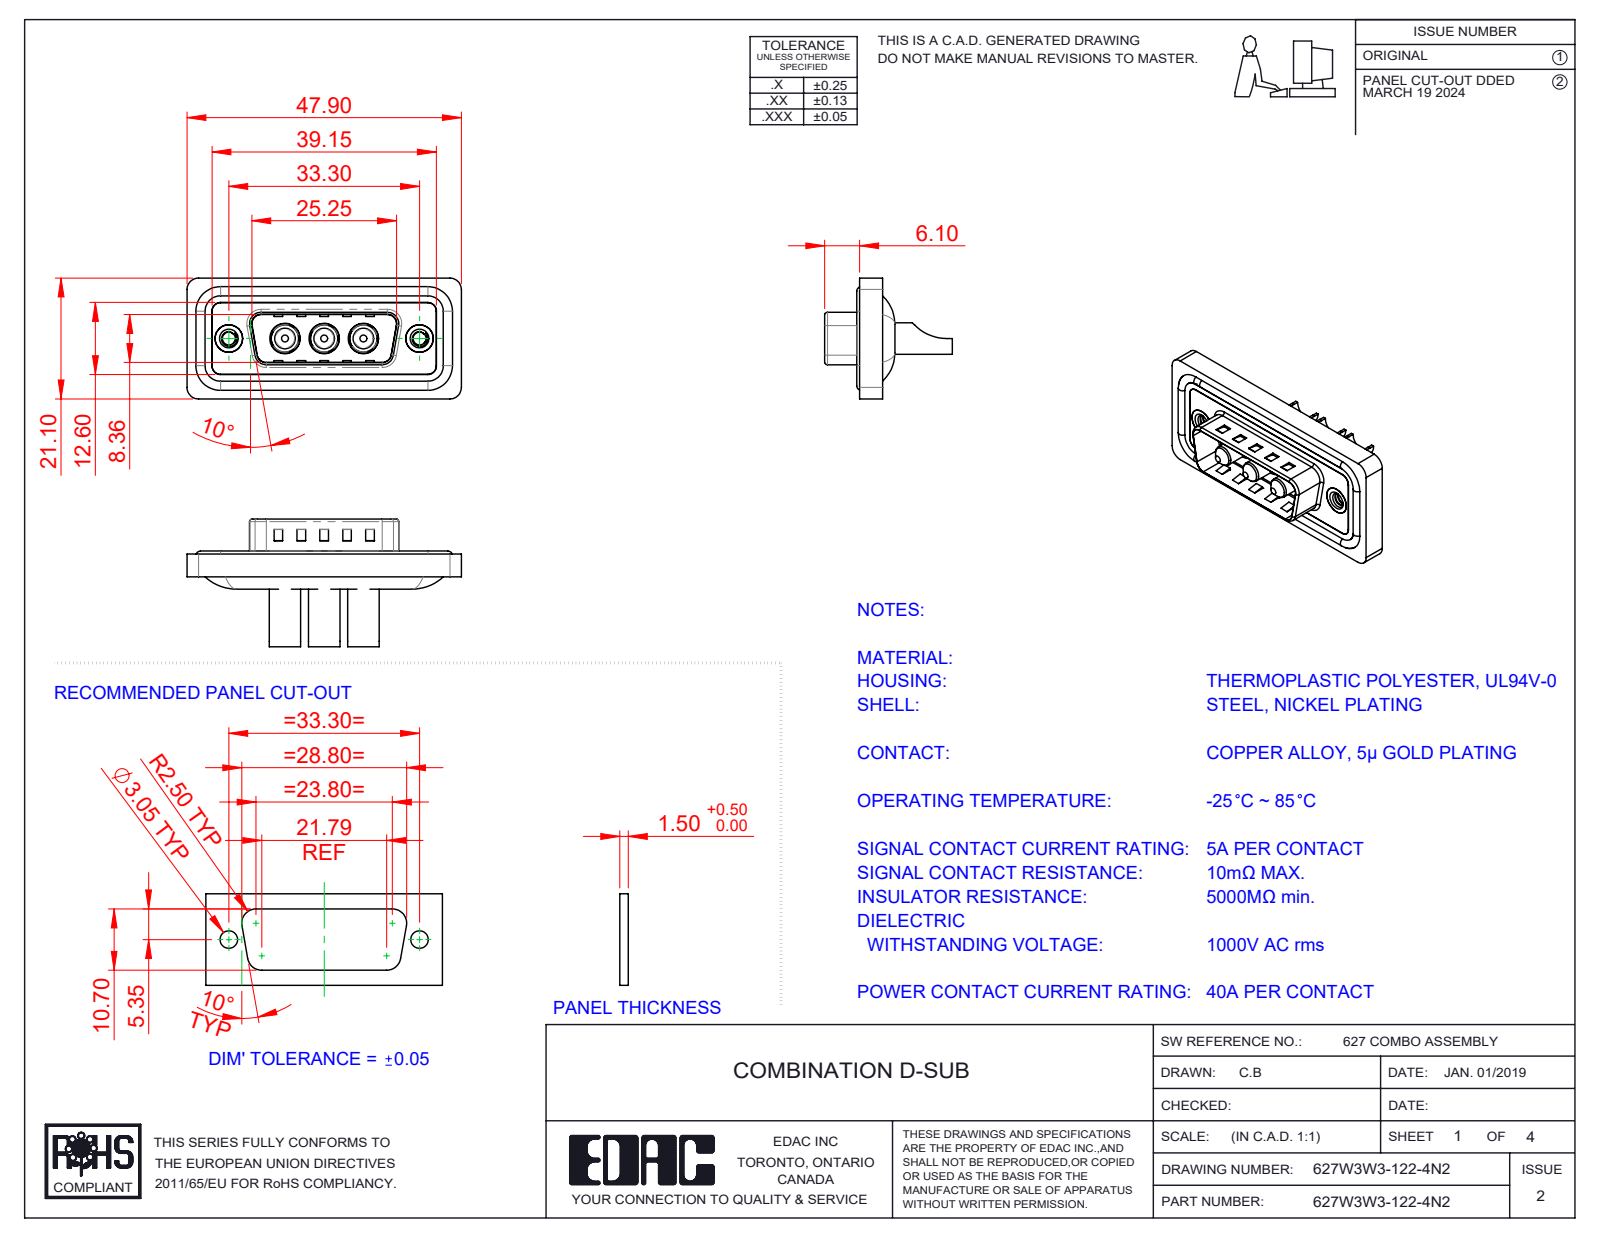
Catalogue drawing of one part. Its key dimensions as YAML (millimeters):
part_name: "Power Pin_40A SC; 627Combo Shell Rear_15 Contacts; 627Combo Threaded Rivet_2; 627Combo Shell Front_15 Contacts (+3 more)"
step_written_by: "SolidWorks 2023 (CONFIG_CONTROL_DESIGN)"
units: millimeters
bodies: {solids: 13, faces: 573, planar: 213, cylindrical: 244, other: 116}
overall_size: [47.9, 22.3, 21.1]
volume: 5705
surface_area: 9173
round_holes:
  - {diameter: 4.6, count: 3}
  - {diameter: 4.85, count: 3}
  - {diameter: 5.3, count: 3}
  - {diameter: 2.26, count: 2}
  - {diameter: 4, count: 2}
  - {diameter: 4.8, count: 2}
  - {diameter: 5, count: 2}
round_bosses_or_shafts:
  - {diameter: 1.6, count: 4}
  - {diameter: 5.5, count: 3}
  - {diameter: 5.2, count: 3}
  - {diameter: 4.75, count: 3}
  - {diameter: 3.75, count: 3}
  - {diameter: 3.6, count: 3}
  - {diameter: 4.9, count: 2}
partial_cylinders:
  - {radius: 1.5, count: 26}
  - {radius: 2, count: 20}
  - {radius: 0.5, count: 8}
  - {radius: 1.6, count: 8}
  - {radius: 0.25, count: 4}
  - {radius: 0.6, count: 4}
  - {radius: 0.65, count: 4}
  - {radius: 0.9, count: 4}
face_to_face_distances: [0.4, 1.1, 0.5, 1.6, 3.1, 2.9, 1.5, 0.82, 9.58, 2.5]
hole_center_spacings: [6.85, 9.8, 16.65, 23.5, 13.7, 33.3]
